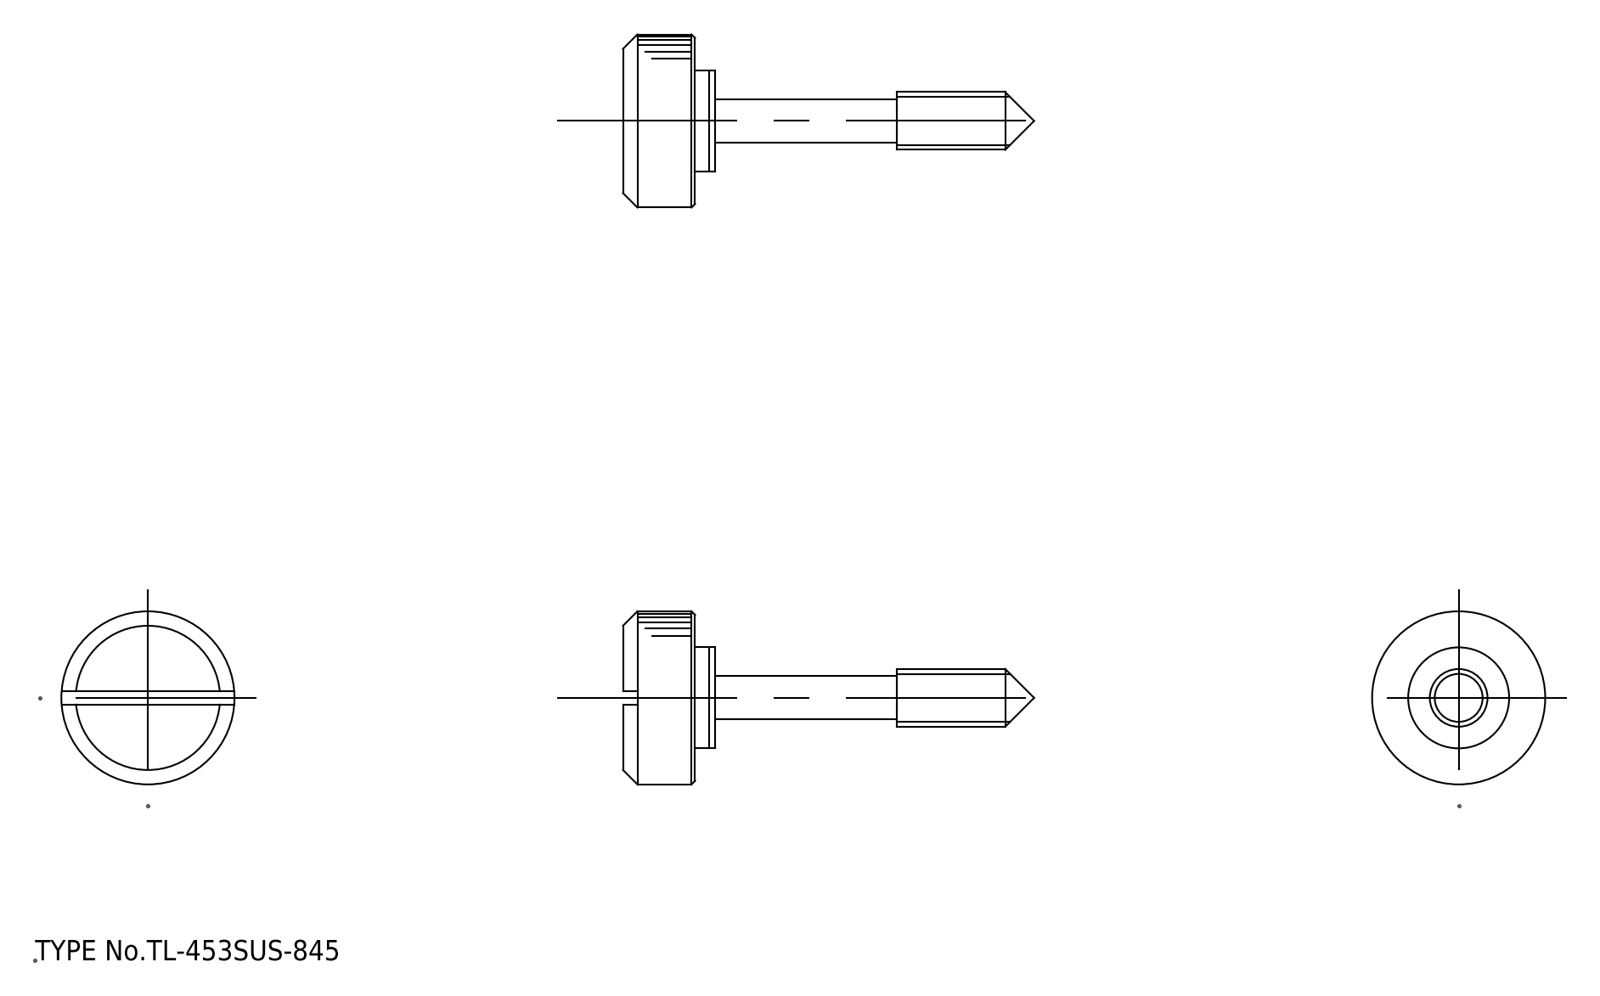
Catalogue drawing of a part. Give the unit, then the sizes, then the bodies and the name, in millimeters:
Units: millimetres
Overall size (bounding box): 57 × 24 × 24
Round bosses / shafts (diameter × count): ⌀24 ×1, ⌀14 ×1, ⌀8 ×1, ⌀6 ×1
Partial cylindrical surfaces — rounded edges, fillets, slot ends (radius × count): R1.25 ×4, R3.05 ×1
Main face-to-face distances: 10, 2, 12, 12.8, 2.8, 0.8, 1.8, 8, 10.8, 38
Volume: 6 246 mm³ · Surface area: 2 923 mm²
Bodies: 2 solids, 42 faces (18 planar, 18 cylindrical, 6 other)
Part name (STEP PRODUCT): washer; knob
STEP written by: spGate 19.8.4 (****-****-****-****) (AUTOMOTIVE_DESIGN)
